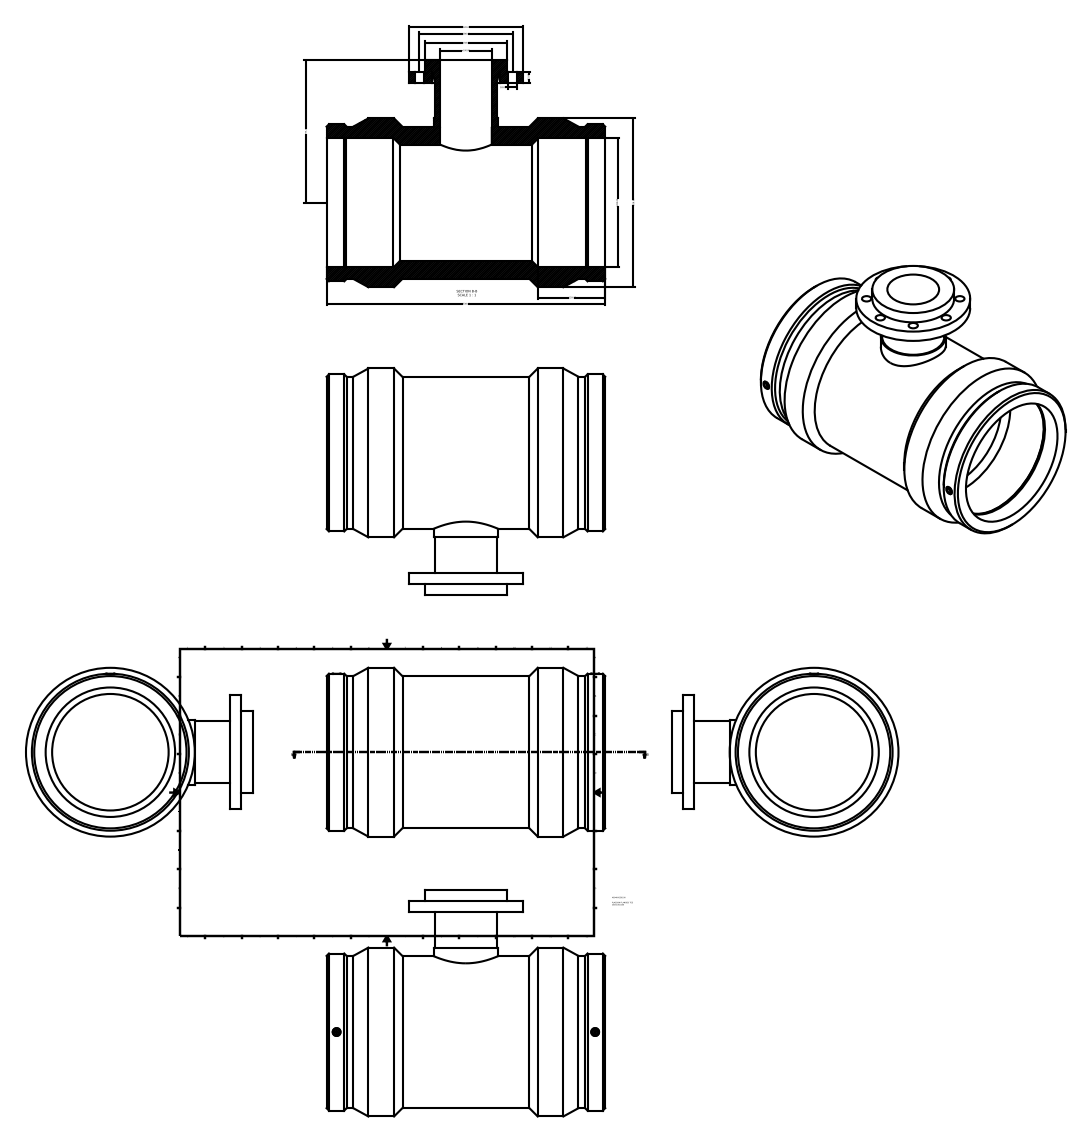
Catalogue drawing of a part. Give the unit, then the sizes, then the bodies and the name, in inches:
Units: inches
Overall size (bounding box): 21.181 × 17.244 × 12.835
Round holes (diameter × count): ⌀0.709 ×8, ⌀0.394 ×2, ⌀3.937 ×1, ⌀5.118 ×1, ⌀8.858 ×1, ⌀9.843 ×1
Round bosses / shafts (diameter × count): ⌀0.157 ×2, ⌀12.835 ×1, ⌀11.936 ×1, ⌀11.578 ×1, ⌀11.551 ×1, ⌀8.661 ×1, ⌀6.22 ×1, ⌀4.921 ×1
Main face-to-face distances: 0.866, 21.181, 1.732, 1.483, 19.698, 4.409, 3.543, 2.677, 18.214, 0.551
Hole centre spacings: 2.712, 3.543, 5.011, 6.547, 7.087, 19.657
Volume: 975.2 in³ · Surface area: 1 803 in²
Bodies: 1 solid, 60 faces (14 planar, 30 cylindrical, 16 other)
Part name (STEP PRODUCT): 499404250100
STEP written by: Autodesk Inventor 2015 (AUTOMOTIVE_DESIGN)
